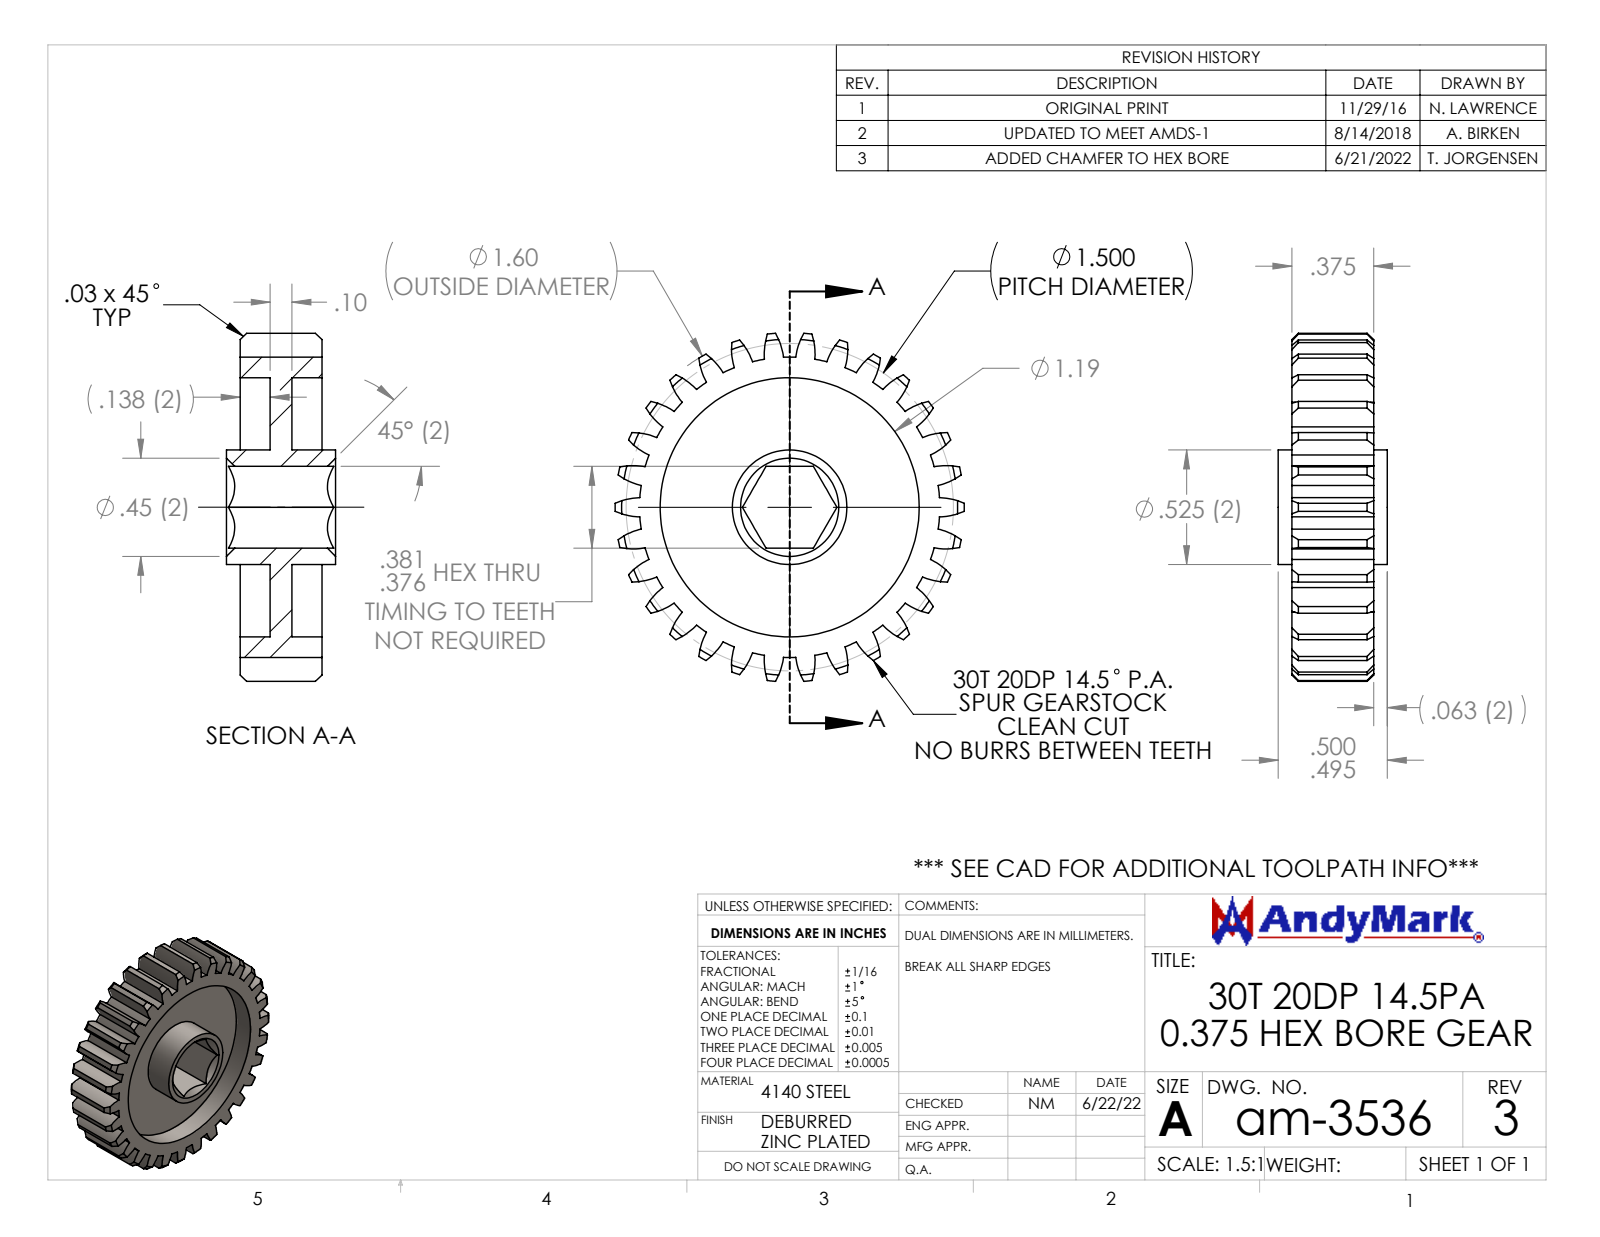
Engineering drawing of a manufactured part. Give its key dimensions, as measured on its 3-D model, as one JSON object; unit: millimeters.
{"part_name": "am-3536 30T 20DP 375hex 375 FW", "step_written_by": "SolidWorks 2021 (CONFIG_CONTROL_DESIGN)", "units": "millimeters", "bodies": {"solids": 1, "faces": 209, "planar": 12, "cylindrical": 133, "other": 64}, "overall_size": [40.6, 40.5, 12.7], "volume_mm3": 5980, "surface_area_mm2": 5865, "round_holes": [[30.1, 1]], "round_bosses_or_shafts": [[13.3, 1]], "partial_cylinders_radius": [[7.6, 60], [17.5, 1], [20.3, 1]], "face_to_face_distances": [2.5, 3.5, 6, 9.5, 6, 3.5, 9.5, 5.1, 7.6, 1.6]}
